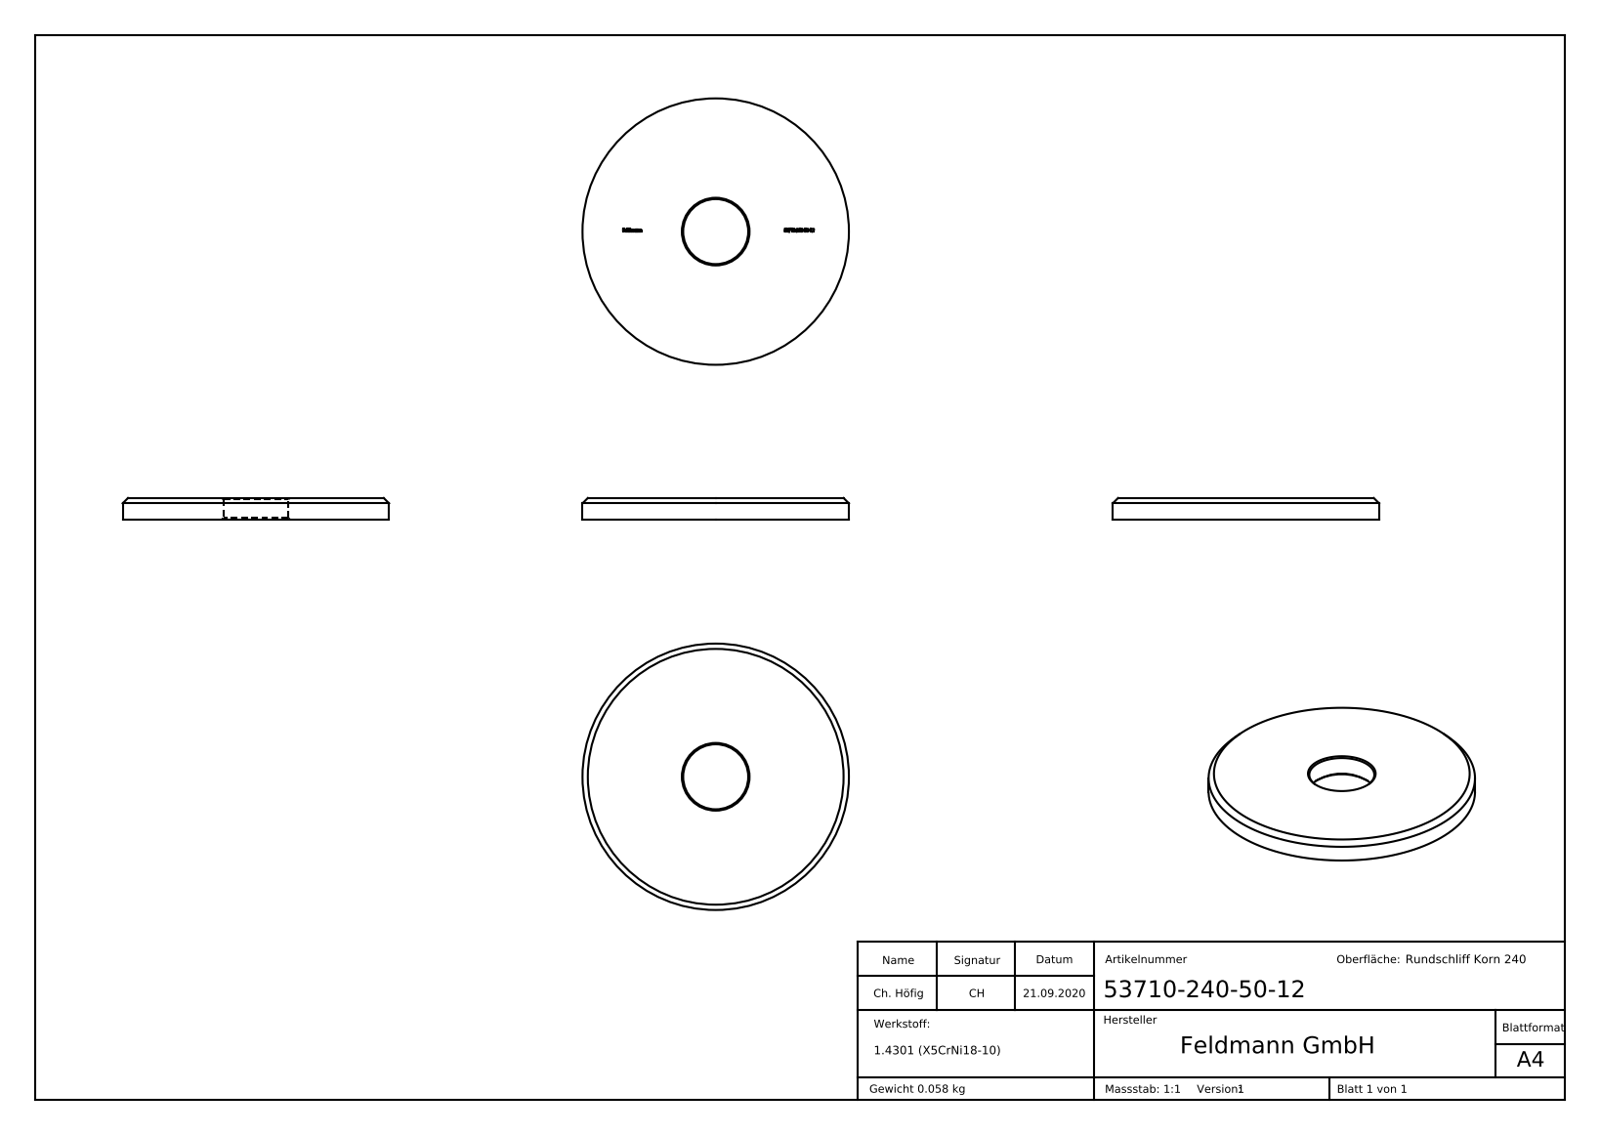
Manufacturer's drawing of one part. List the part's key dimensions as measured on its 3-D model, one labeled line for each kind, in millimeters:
Part name (STEP PRODUCT): 53710-240-50-12
STEP written by: SolidWorks 2018 (CONFIG_CONTROL_DESIGN)
Units: millimetres
Bodies: 1 solid, 283 faces (156 planar, 4 cylindrical, 123 other)
Overall size (bounding box): 50 × 50 × 4
Volume: 7 306 mm³ · Surface area: 4 375 mm²
Round holes (diameter × count): ⌀12.2 ×1
Round bosses / shafts (diameter × count): ⌀50 ×1
Main face-to-face distances: 4, 3.9, 0.35, 0.53, 0.55, 0.5, 30.85, 34.43, 3.58, 0.47
